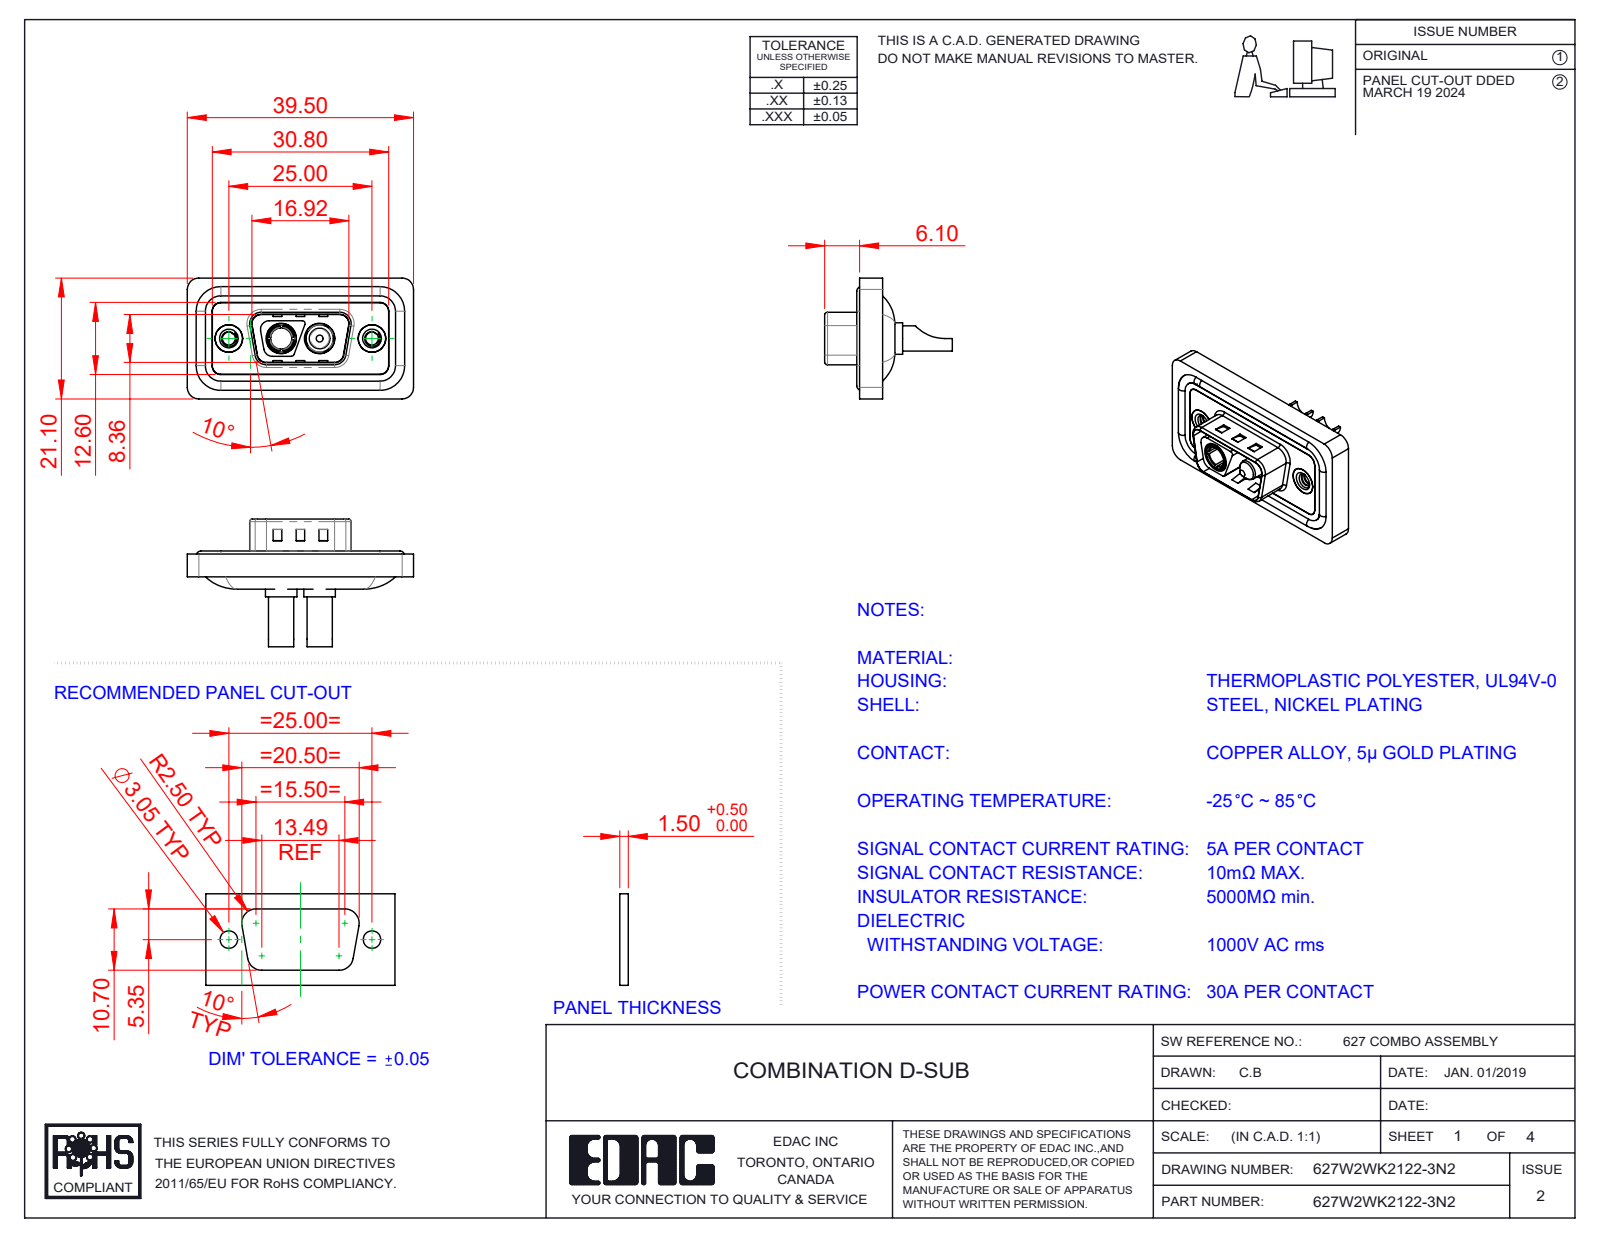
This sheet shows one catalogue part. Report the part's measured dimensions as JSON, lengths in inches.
{"part_name": "Power Socket_30A SC; 627W2WK2122-3N2; 627Combo Housing_2WK2; 627Combo Threaded Rivet_2 (+4 more)", "step_written_by": "SolidWorks 2023 (CONFIG_CONTROL_DESIGN)", "units": "inches", "bodies": {"solids": 11, "faces": 546, "planar": 195, "cylindrical": 233, "other": 118}, "overall_size": [1.555, 0.878, 0.831], "volume_in3": 0.281, "surface_area_in2": 11.71, "round_holes": [[0.089, 2], [0.138, 2], [0.157, 2], [0.189, 2], [0.191, 2], [0.197, 2], [0.209, 2], [0.146, 1]], "round_bosses_or_shafts": [[0.063, 4], [0.217, 2], [0.205, 2], [0.193, 2], [0.187, 2], [0.173, 2], [0.148, 2], [0.195, 1]], "partial_cylinders_radius": [[0.059, 24], [0.079, 18], [0.02, 10], [0.063, 8], [0.01, 4], [0.024, 4], [0.026, 4], [0.035, 4]], "face_to_face_distances": [0.016, 0.043, 0.114, 0.02, 0.122, 0.063, 0.059, 0.098, 0.071, 0.126], "hole_center_spacings": [0.36, 0.624, 0.265, 0.984]}
